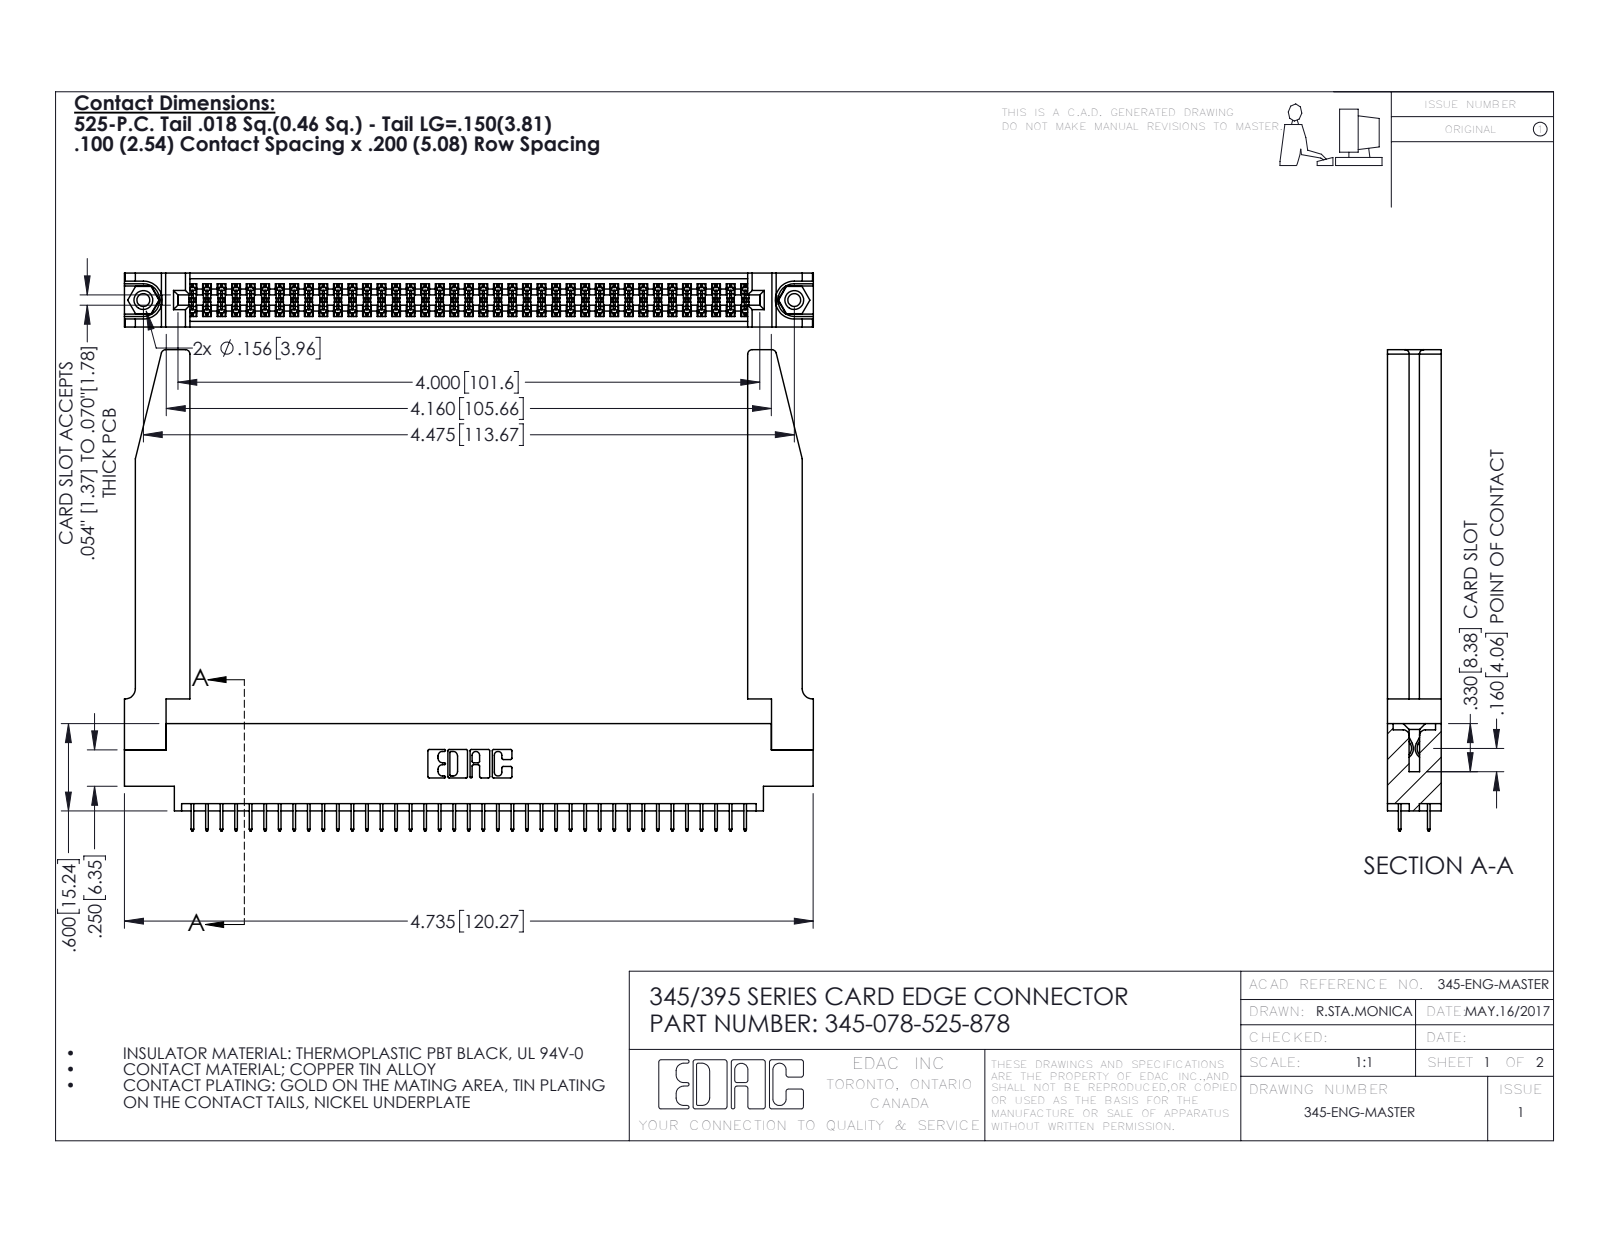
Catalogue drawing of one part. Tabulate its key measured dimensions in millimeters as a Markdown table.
| quantity | value |
| --- | --- |
| part name | 345-078-525-878; 345-250-001_345-250-001-102; 345 Part_0.170 Offset - 0.156 Dia-TH; 345-292-001_345-293-125 (+1 more) |
| STEP written by | SolidWorks 2020 (CONFIG_CONTROL_DESIGN) |
| units | millimeters |
| bodies | 83 solids, 4576 faces (3268 planar, 1256 cylindrical, 52 other) |
| overall size | 120.3 × 84 × 9.4 |
| volume | 19 190 mm³ |
| surface area | 23 410 mm² |
| round holes (diameter × count) | 2.3 × 2, 3.2 × 2, 4 × 2, 1.6 × 1 |
| round bosses / shafts (diameter × count) | 3.9 × 2 |
| partial cylindrical surfaces (radius × count) | 0.2 × 117, 0.3 × 22, 0.8 × 8, 0.2 × 6, 0.8 × 6, 0.7 × 3, 0.4 × 2, 0.5 × 2 |
| main face-to-face distances | 9.4, 1.8, 7.6, 5.1, 2.5, 6.9, 0.6, 5.7, 4.4, 3.8 |
| hole center spacings | 6.9, 107.7, 113.7 |
